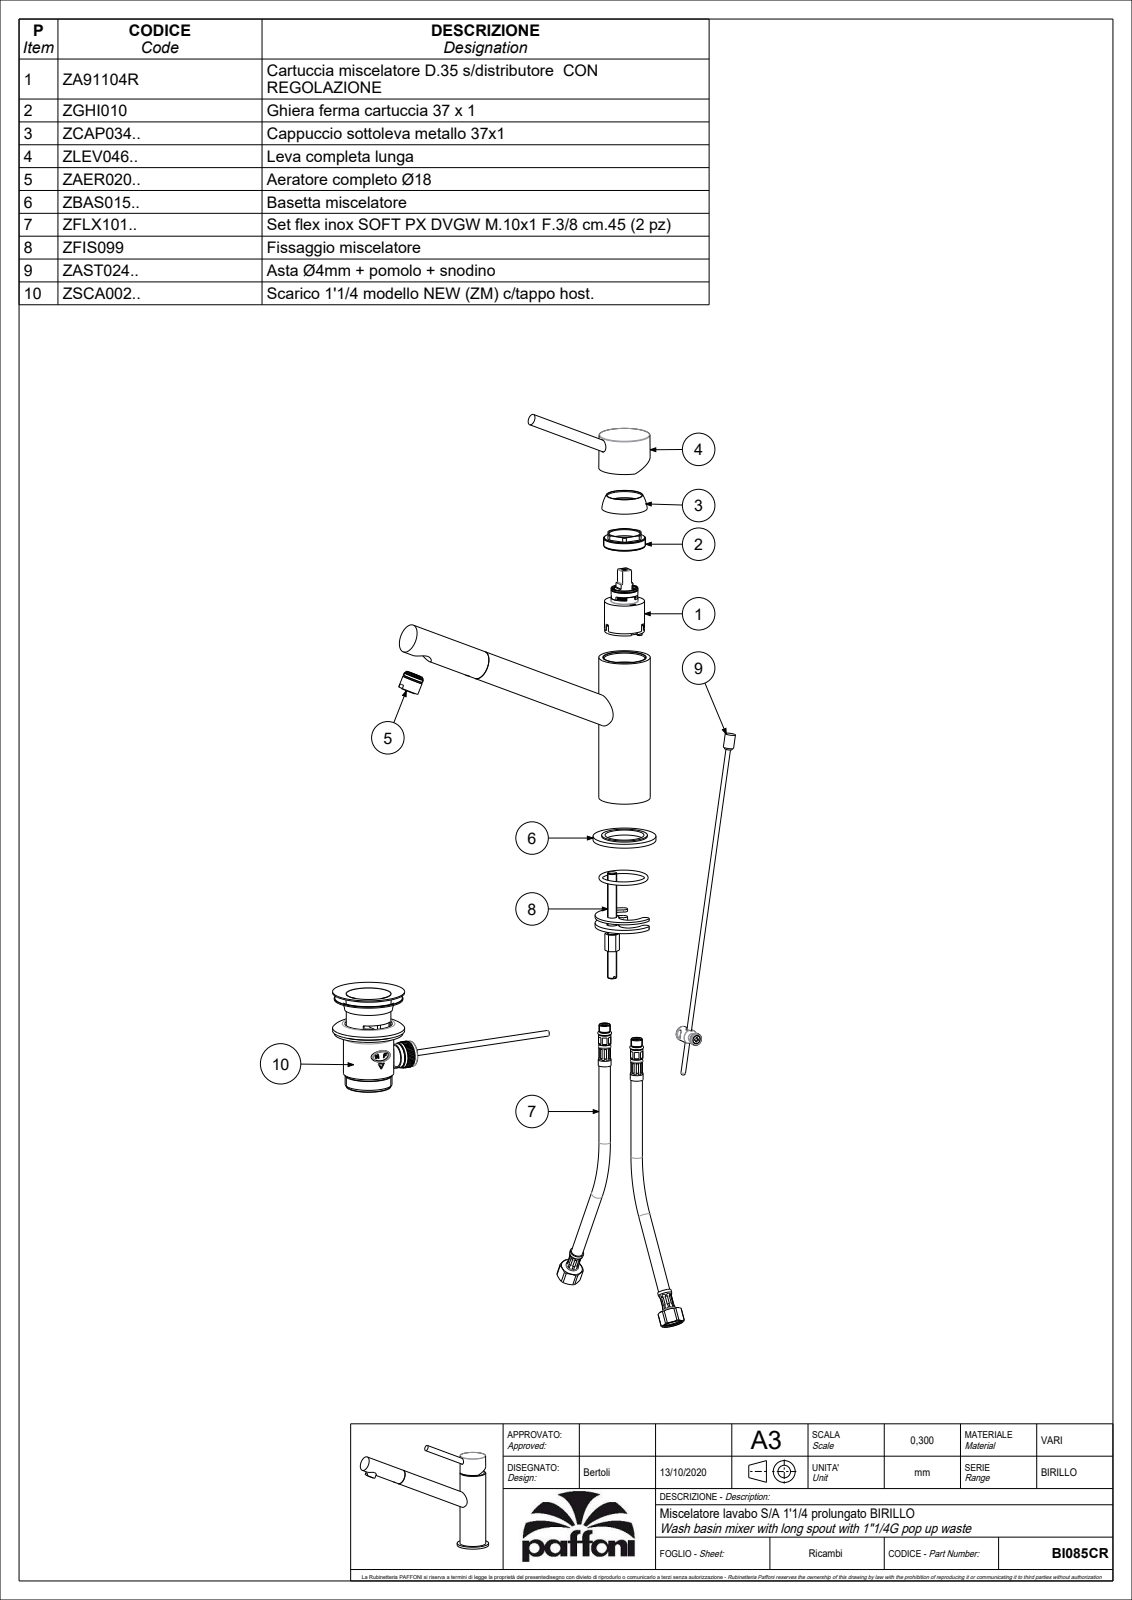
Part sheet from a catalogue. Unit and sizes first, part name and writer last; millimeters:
Units: millimetres
Overall size (bounding box): 258.1 × 192.84 × 55
Round holes (diameter × count): ⌀5 ×4, ⌀6.5 ×3, ⌀9 ×3, ⌀11 ×3, ⌀4 ×2, ⌀4.5 ×2, ⌀8 ×2, ⌀18.4 ×2, ⌀3.3 ×1, ⌀5.5 ×1, ⌀7.25 ×1, ⌀10 ×1
Round bosses / shafts (diameter × count): ⌀12 ×2, ⌀10 ×2, ⌀6.5 ×2, ⌀4 ×2, ⌀55 ×1, ⌀45 ×1, ⌀40 ×1, ⌀35 ×1
Partial cylindrical surfaces — rounded edges, fillets, slot ends (radius × count): R0.5 ×36, R3 ×29, R0.15 ×11, R0.3 ×4, R1 ×2, R1.05 ×1, R5 ×1, R7 ×1
Main face-to-face distances: 26.5, 96, 23, 132.1, 3.5, 99.5, 73, 4.5, 5.5, 121.5
Hole centre spacings: 3.54, 8.06, 8.75, 9.88, 10.39, 10.97, 11.05, 11.95
Volume: 239 968 mm³ · Surface area: 100 982 mm²
Bodies: 4 solids, 1262 faces (624 planar, 361 cylindrical, 277 other)
Part name (STEP PRODUCT): BI085CR
STEP written by: CREO PARAMETRIC BY PTC INC, 2020044 (CONFIG_CONTROL_DESIGN)
